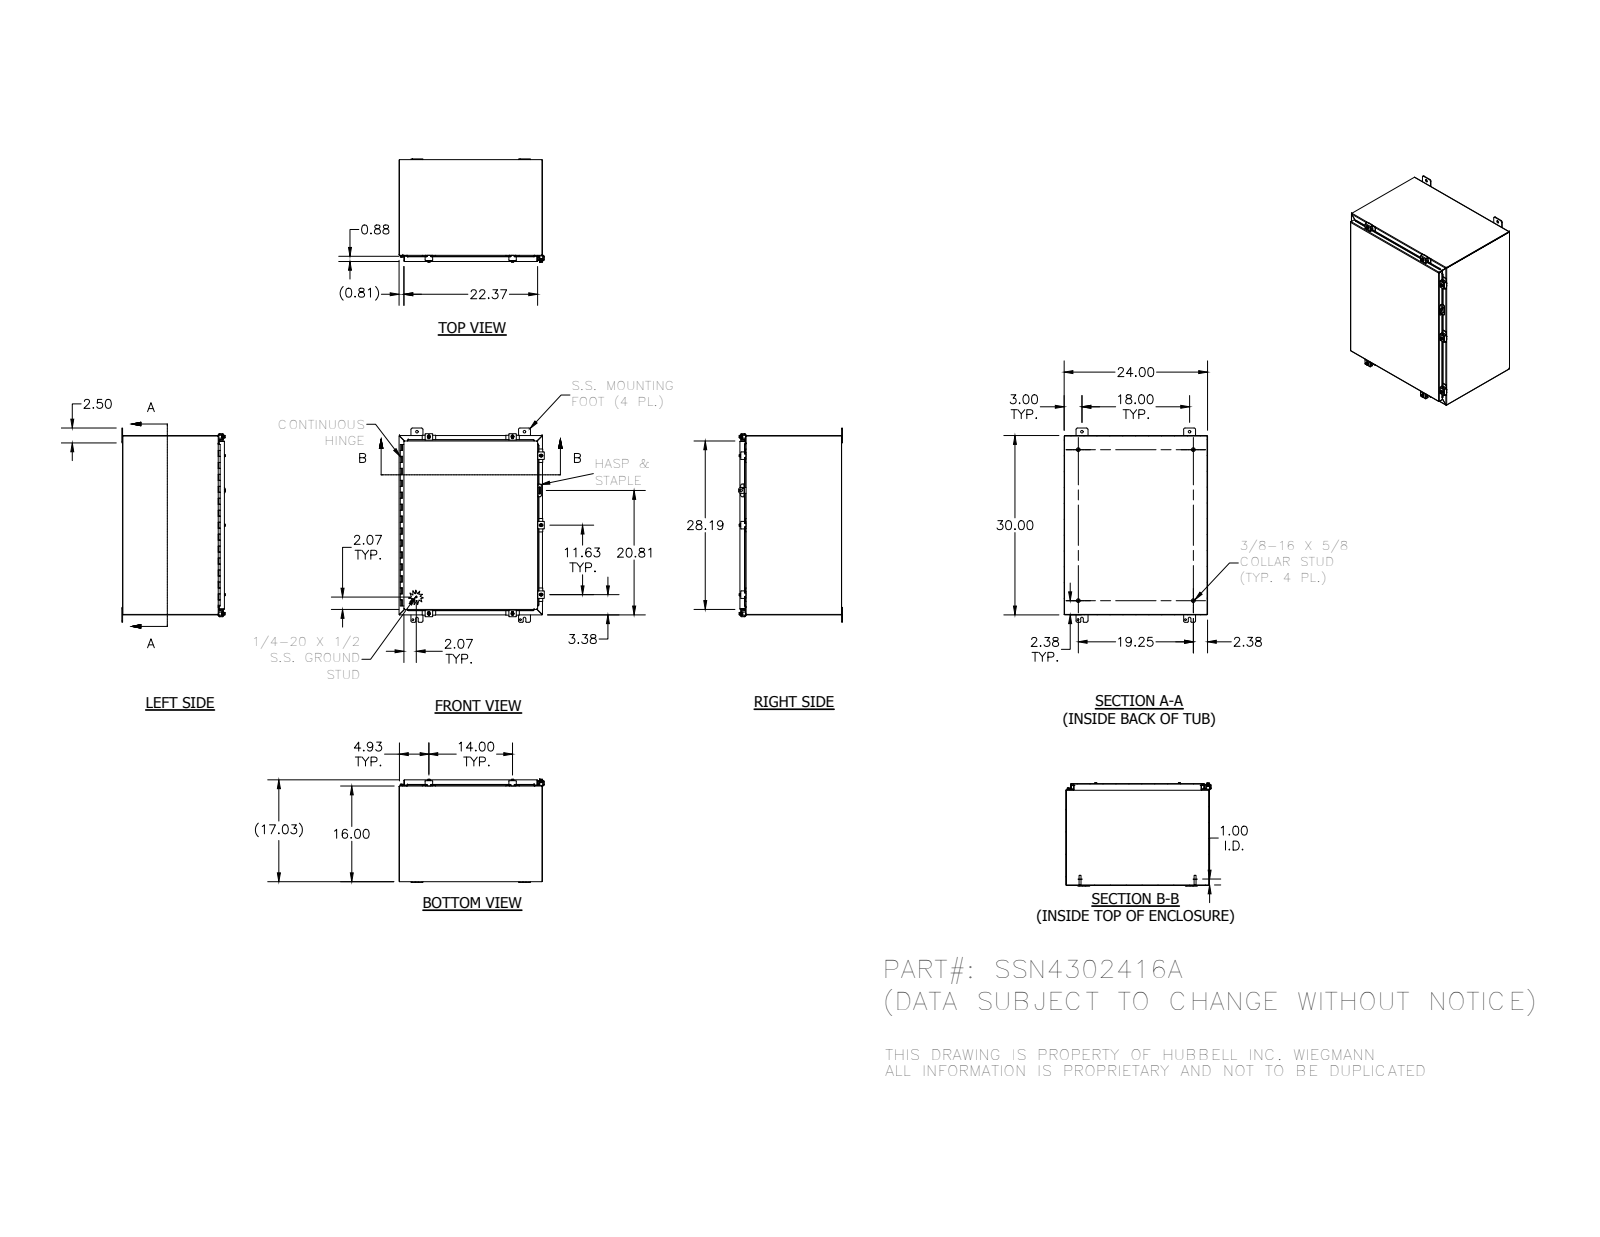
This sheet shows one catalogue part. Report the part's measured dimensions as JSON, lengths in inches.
{"part_name": "SSN4302416ALRS; 34839; 3298; 38859 (+8 more)", "step_written_by": "SolidWorks 2014 (AUTOMOTIVE_DESIGN)", "units": "inches", "bodies": {"solids": 54, "faces": 1942, "planar": 798, "cylindrical": 841, "other": 303}, "overall_size": [32.5, 24.311, 17.355], "volume_in3": 271.2, "surface_area_in2": 7191, "round_holes": [[0.211, 7], [0.281, 7], [0.3, 7], [0.313, 4], [0.438, 4], [0.125, 1], [0.156, 1], [0.5, 1]], "round_bosses_or_shafts": [[0.25, 9], [0.52, 7], [0.5, 7], [0.35, 7], [0.625, 4], [0.33, 4], [0.337, 1], [0.12, 1]], "partial_cylinders_radius": [[0.03, 83], [0.125, 37], [0.25, 33], [0.031, 21], [0.105, 21], [0.062, 18], [0.141, 14], [0.1, 10]], "face_to_face_distances": [0.074, 16.959, 23.926, 29.926, 16.885, 17.033, 23.852, 24, 29.852, 30], "hole_center_spacings": [1.593, 18, 30, 34.986, 2.046, 2.16, 14, 15.57]}
